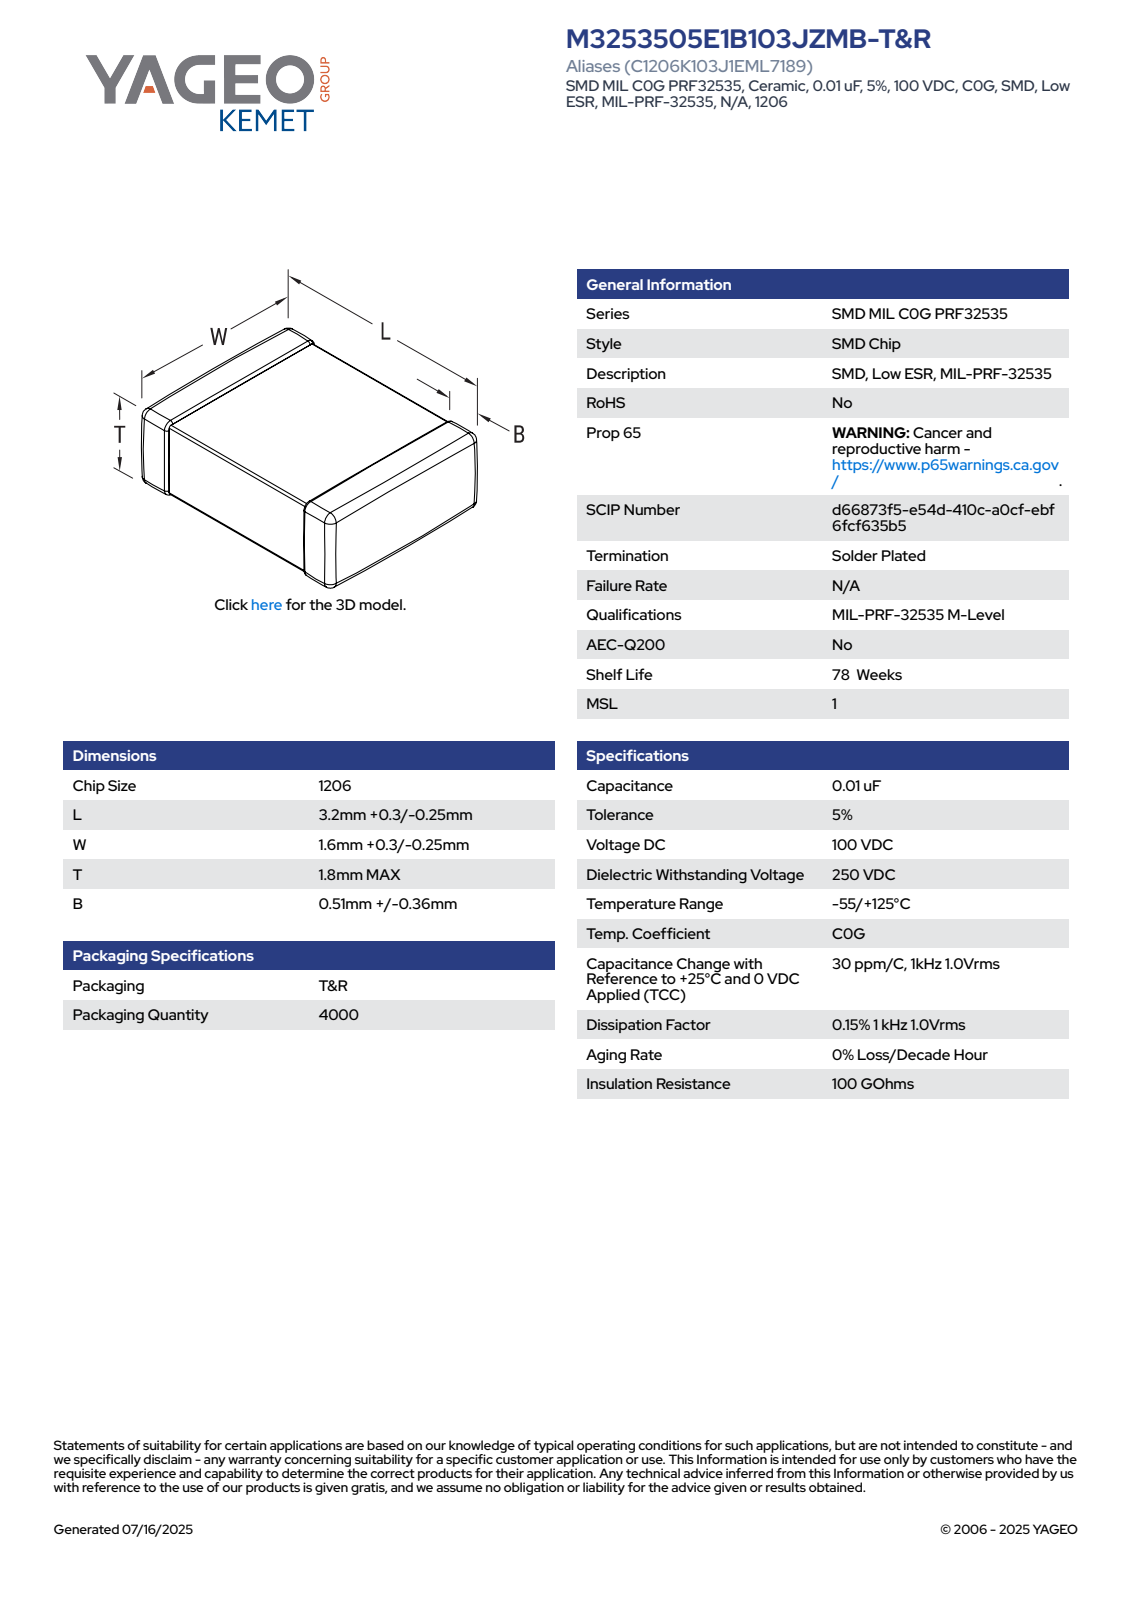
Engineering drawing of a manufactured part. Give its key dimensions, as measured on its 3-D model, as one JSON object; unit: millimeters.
{"part_name": "CCS_STDNOS_1206_L3.5W1.9T1.8B0.51", "step_written_by": "SolidWorks 2021 (AUTOMOTIVE_DESIGN)", "units": "millimeters", "bodies": {"solids": 4, "faces": 129, "planar": 71, "cylindrical": 42, "other": 16}, "overall_size": [3.5, 1.9, 1.8], "volume_mm3": 11, "surface_area_mm2": 32, "face_to_face_distances": [1.72, 1.82, 1.76, 3.5, 1.86, 1.8, 1.9, 1.77, 1.73, 0.33]}
